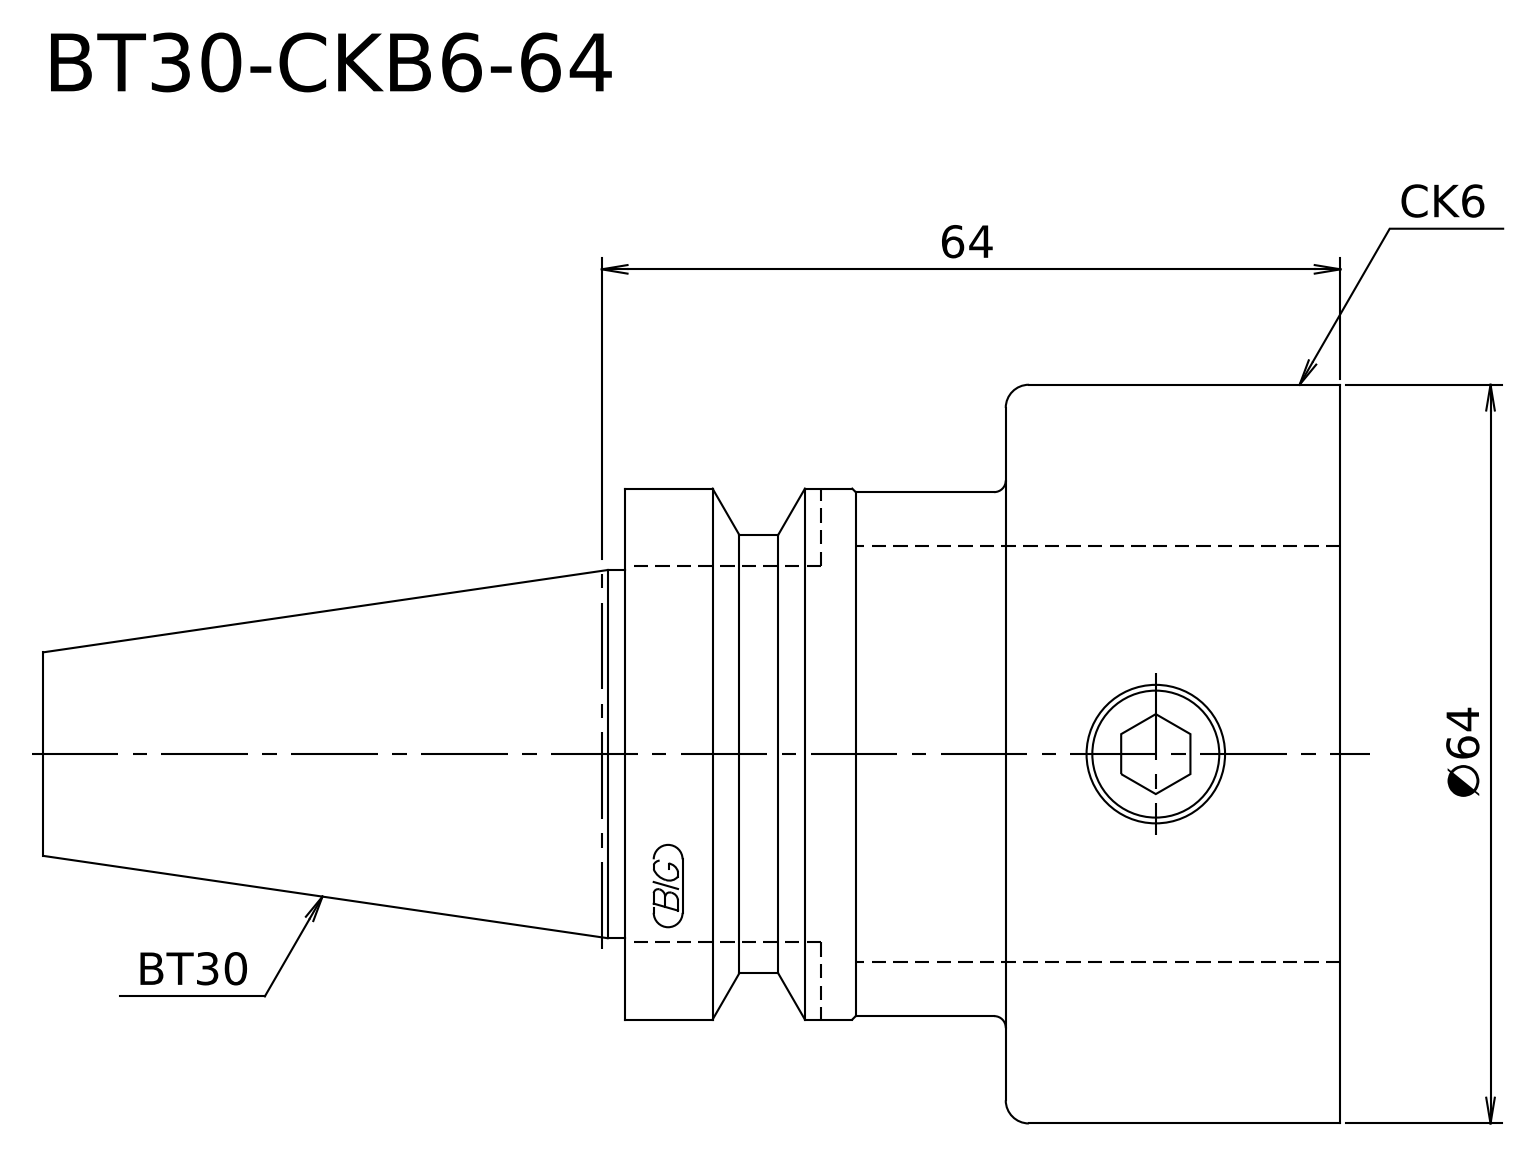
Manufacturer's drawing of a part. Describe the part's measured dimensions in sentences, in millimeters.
Its 3-D file was written by "Kubotek KeyCreator V8.5.1 (14335) (CONFIG_CONTROL_DESIGN)". It is 1 solid with 15 faces: 4 planar, 6 cylindrical and 5 other. Overall it measures 112.4 by 64 by 64 millimeters. Its volume is 170 237 cubic millimeters and its surface area 20 815 square millimeters. Round bosses or shafts: 1 of diameter 64, 1 of diameter 46, 1 of diameter 45.4, 1 of diameter 38, 1 of diameter 31.9. The main face-to-face distances are 29, 62, 33, 112.4, 83.4, 50.4.
